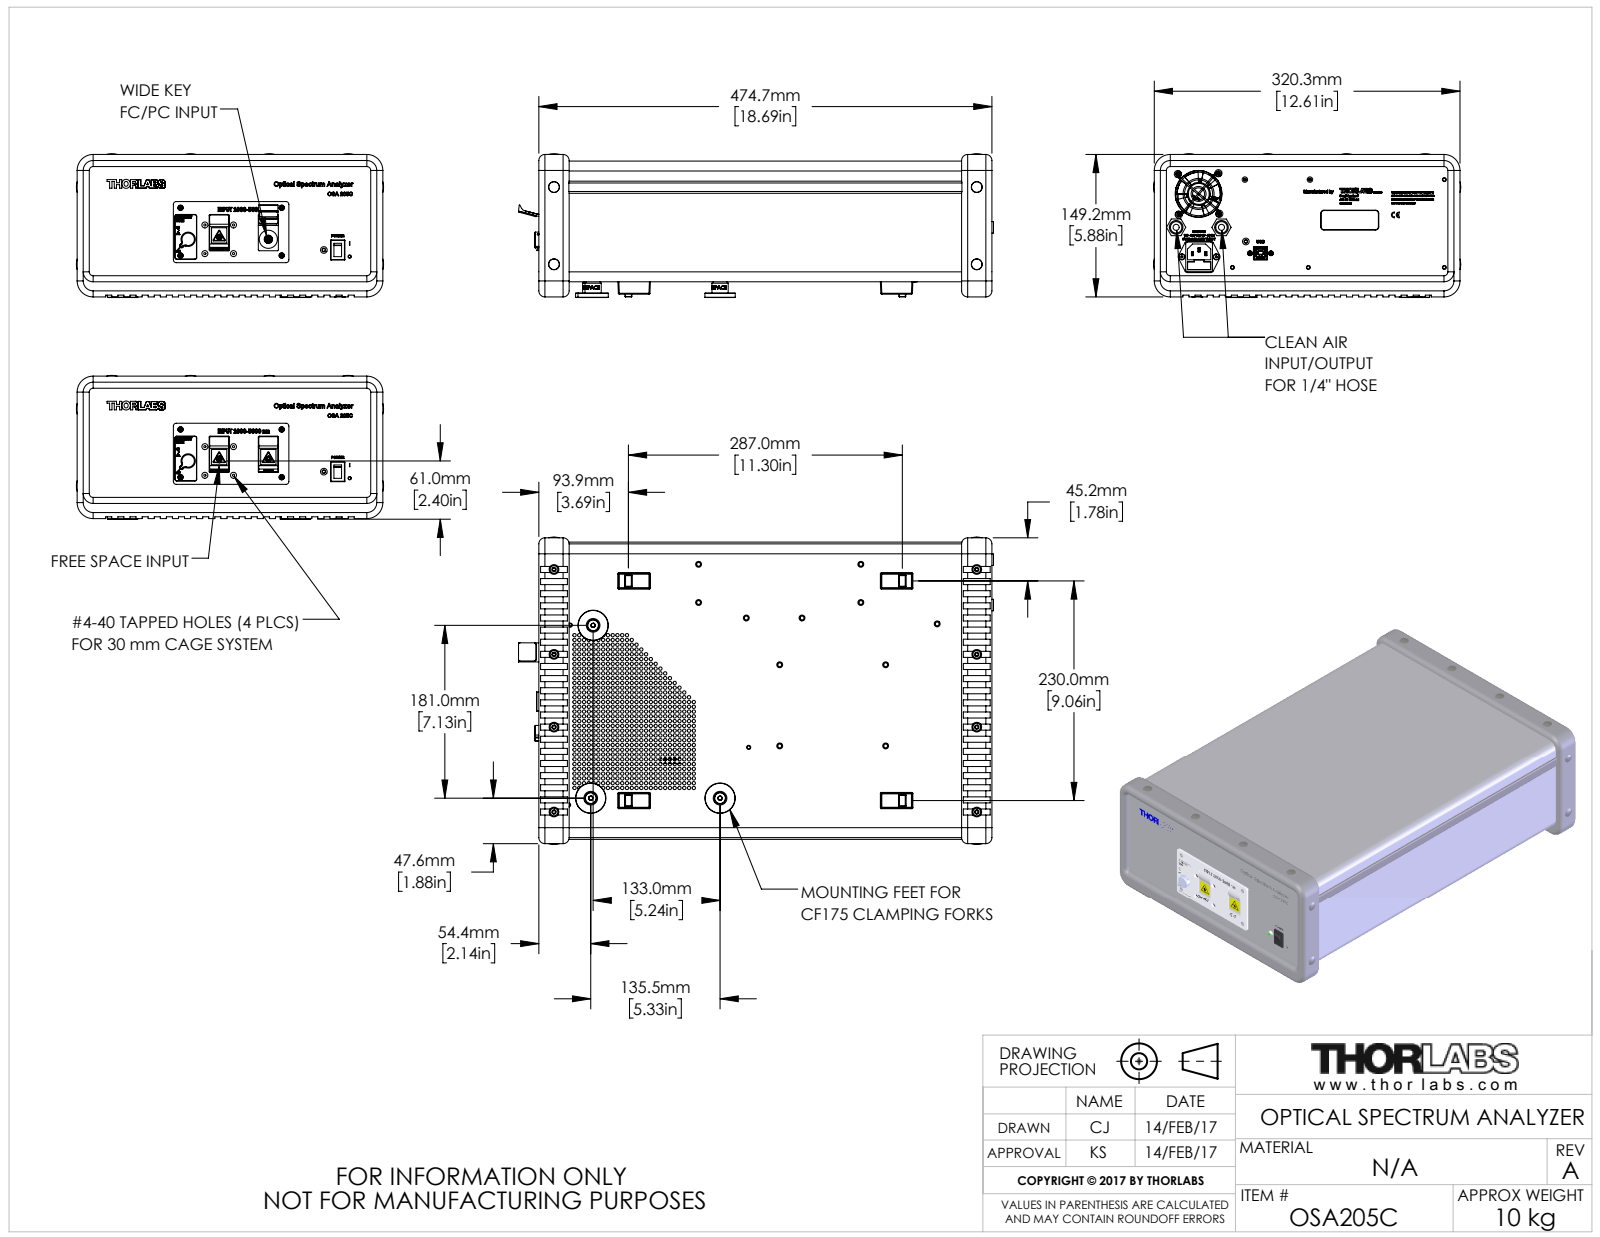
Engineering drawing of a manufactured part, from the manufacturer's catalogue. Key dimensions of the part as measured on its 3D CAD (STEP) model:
Part name (STEP PRODUCT): MKD 110 0430_ppen FREE-SPACE; NEO40701N; FKK 301 0006; S-M4-1 (+8 more)
STEP written by: SolidWorks 2016 (AUTOMOTIVE_DESIGN)
Units: millimetres
Bodies: 254 solids, 17523 faces (8896 planar, 3970 cylindrical, 4657 other)
Overall size (bounding box): 480.91 × 321.82 × 150.61
Volume: 1 900 000 mm³ · Surface area: 1 632 000 mm²
Round holes (diameter × count): ⌀3.5 ×753, ⌀2.5 ×49, ⌀2.05 ×28, ⌀3.2 ×26, ⌀3.3 ×17, ⌀3 ×15, ⌀2.26 ×13, ⌀1.2 ×12, ⌀5.08 ×12, ⌀11.43 ×12, ⌀5 ×11, ⌀3.1 ×9
Round bosses / shafts (diameter × count): ⌀3 ×36, ⌀4 ×22, ⌀5 ×20, ⌀6 ×17, ⌀7 ×15, ⌀2.4 ×13, ⌀11.05 ×12, ⌀5.38 ×12
Partial cylindrical surfaces — rounded edges, fillets, slot ends (radius × count): R0.5 ×91, R1 ×56, R0.27 ×48, R0.91 ×48, R1.5 ×47, R3 ×40, R0.16 ×24, R0.55 ×24
Main face-to-face distances: 1, 125.4, 126.4, 124.4, 306.6, 461, 90.65, 34.75, 307.6, 305.6
Hole centre spacings: 16, 25.5, 32, 105, 275.05, 5, 10, 230
